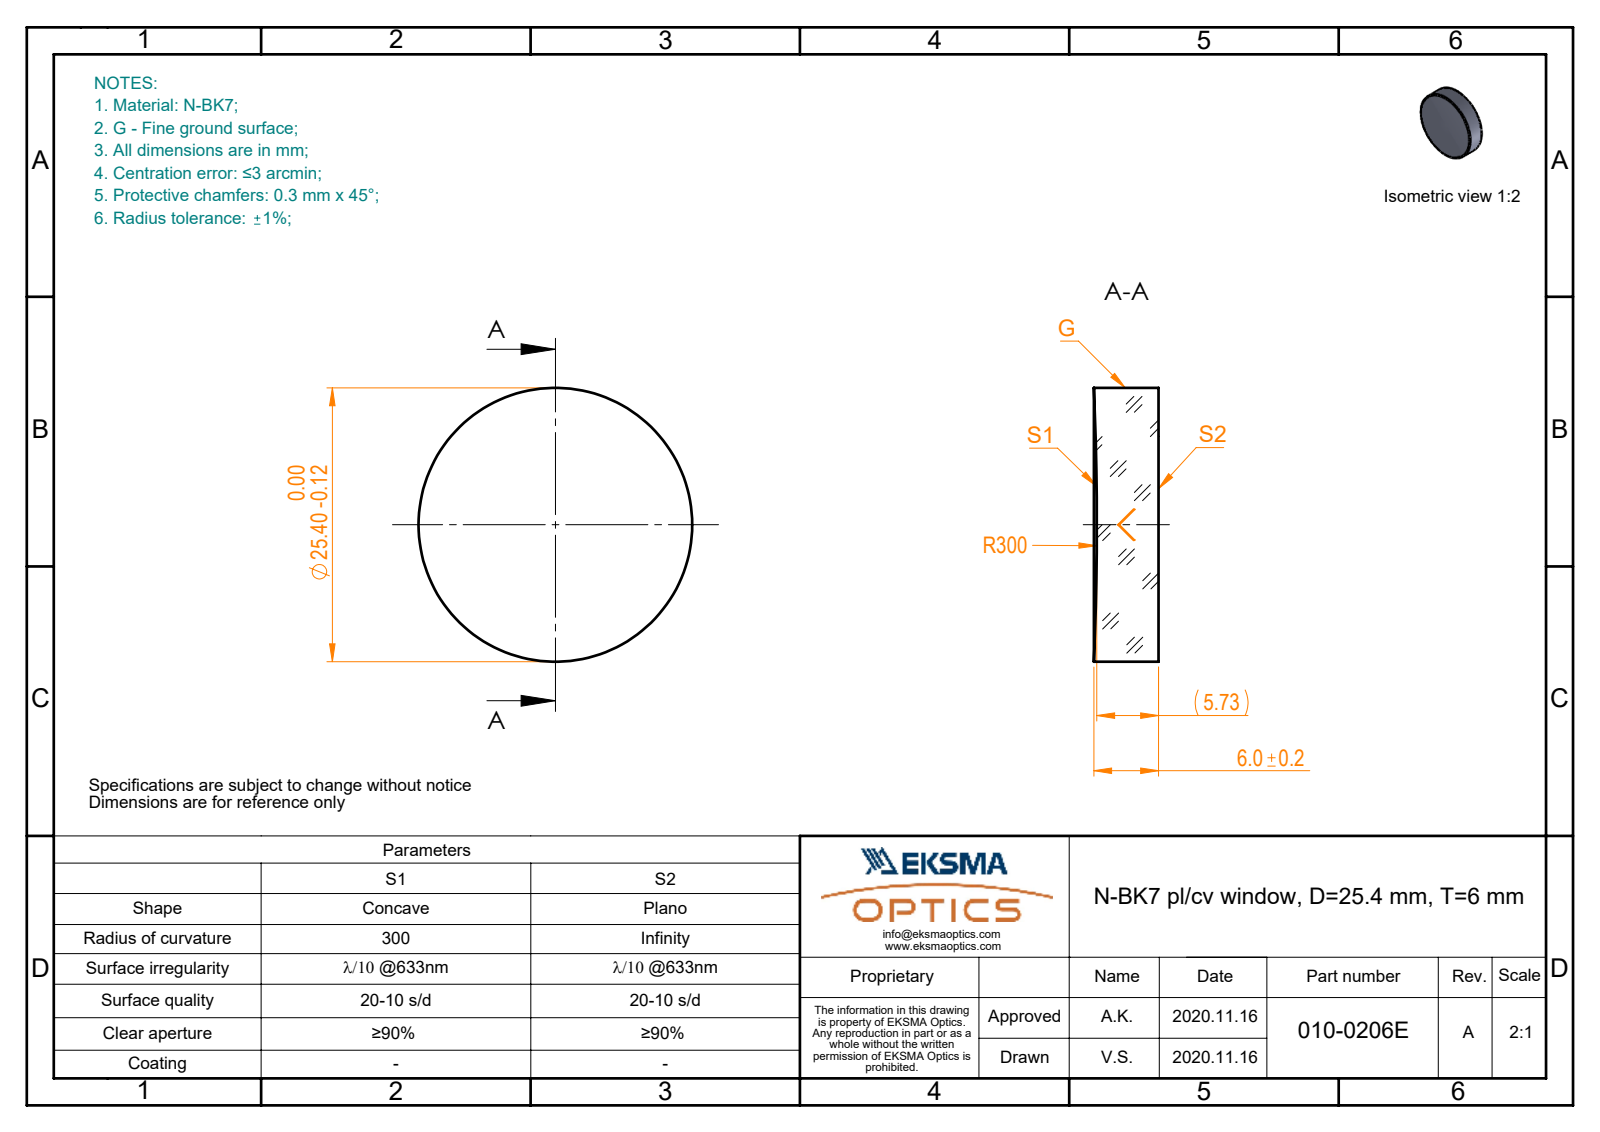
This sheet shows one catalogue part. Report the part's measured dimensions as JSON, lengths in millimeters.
{"part_name": "010-0206E_N-BK7_PCV_window", "step_written_by": "SolidWorks 2019 (CONFIG_CONTROL_DESIGN)", "units": "millimeters", "bodies": {"solids": 1, "faces": 5, "planar": 1, "cylindrical": 2, "other": 2}, "overall_size": [25.4, 25.4, 6], "volume_mm3": 2972, "surface_area_mm2": 1492, "round_bosses_or_shafts": [[25.4, 1]]}
